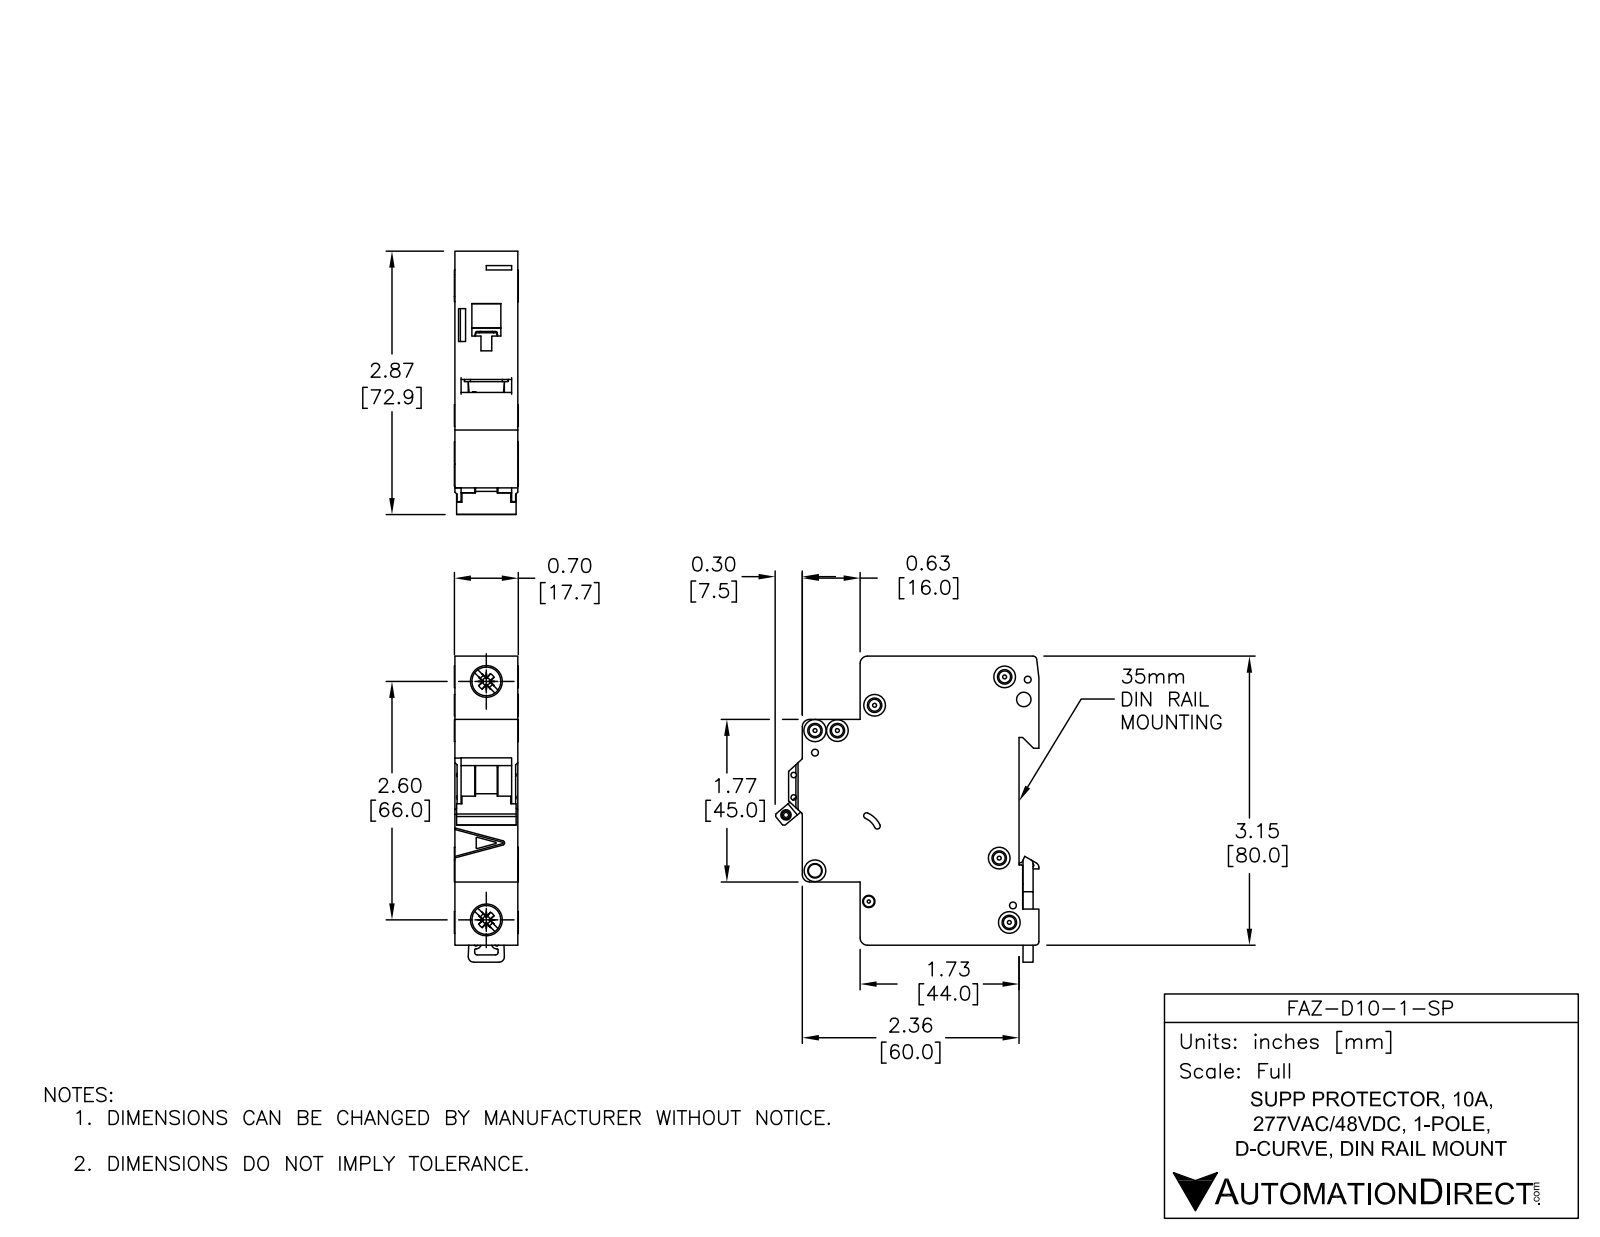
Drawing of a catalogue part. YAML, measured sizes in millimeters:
part_name: "FAZ-D10-1-SP"
step_written_by: "SolidWorks 2014 (AUTOMOTIVE_DESIGN)"
units: millimeters
bodies: {solids: 5, faces: 558, planar: 235, cylindrical: 202, other: 121}
overall_size: [84.78, 73.04, 17.7]
volume: 74935
surface_area: 19545
round_holes:
  - {diameter: 3.6, count: 6}
  - {diameter: 1.9, count: 3}
  - {diameter: 1.09, count: 2}
  - {diameter: 1.5, count: 2}
  - {diameter: 4, count: 2}
  - {diameter: 7.15, count: 2}
  - {diameter: 2.15, count: 1}
  - {diameter: 2.2, count: 1}
  - {diameter: 2.55, count: 1}
  - {diameter: 3.3, count: 1}
  - {diameter: 3.4, count: 1}
round_bosses_or_shafts:
  - {diameter: 6, count: 4}
  - {diameter: 8.2, count: 2}
  - {diameter: 2.5, count: 1}
partial_cylinders:
  - {radius: 0.25, count: 30}
  - {radius: 0.5, count: 13}
  - {radius: 2, count: 8}
  - {radius: 0.2, count: 5}
  - {radius: 1, count: 4}
  - {radius: 0.8, count: 2}
  - {radius: 3, count: 2}
  - {radius: 1.5, count: 1}
face_to_face_distances: [17.5, 79.48, 5.5, 49.5, 44, 65.5, 60, 16, 1.75, 15.75]
hole_center_spacings: [6.2, 13.64, 4.81, 5.19, 5.61, 6.1, 6.44, 8.19]
